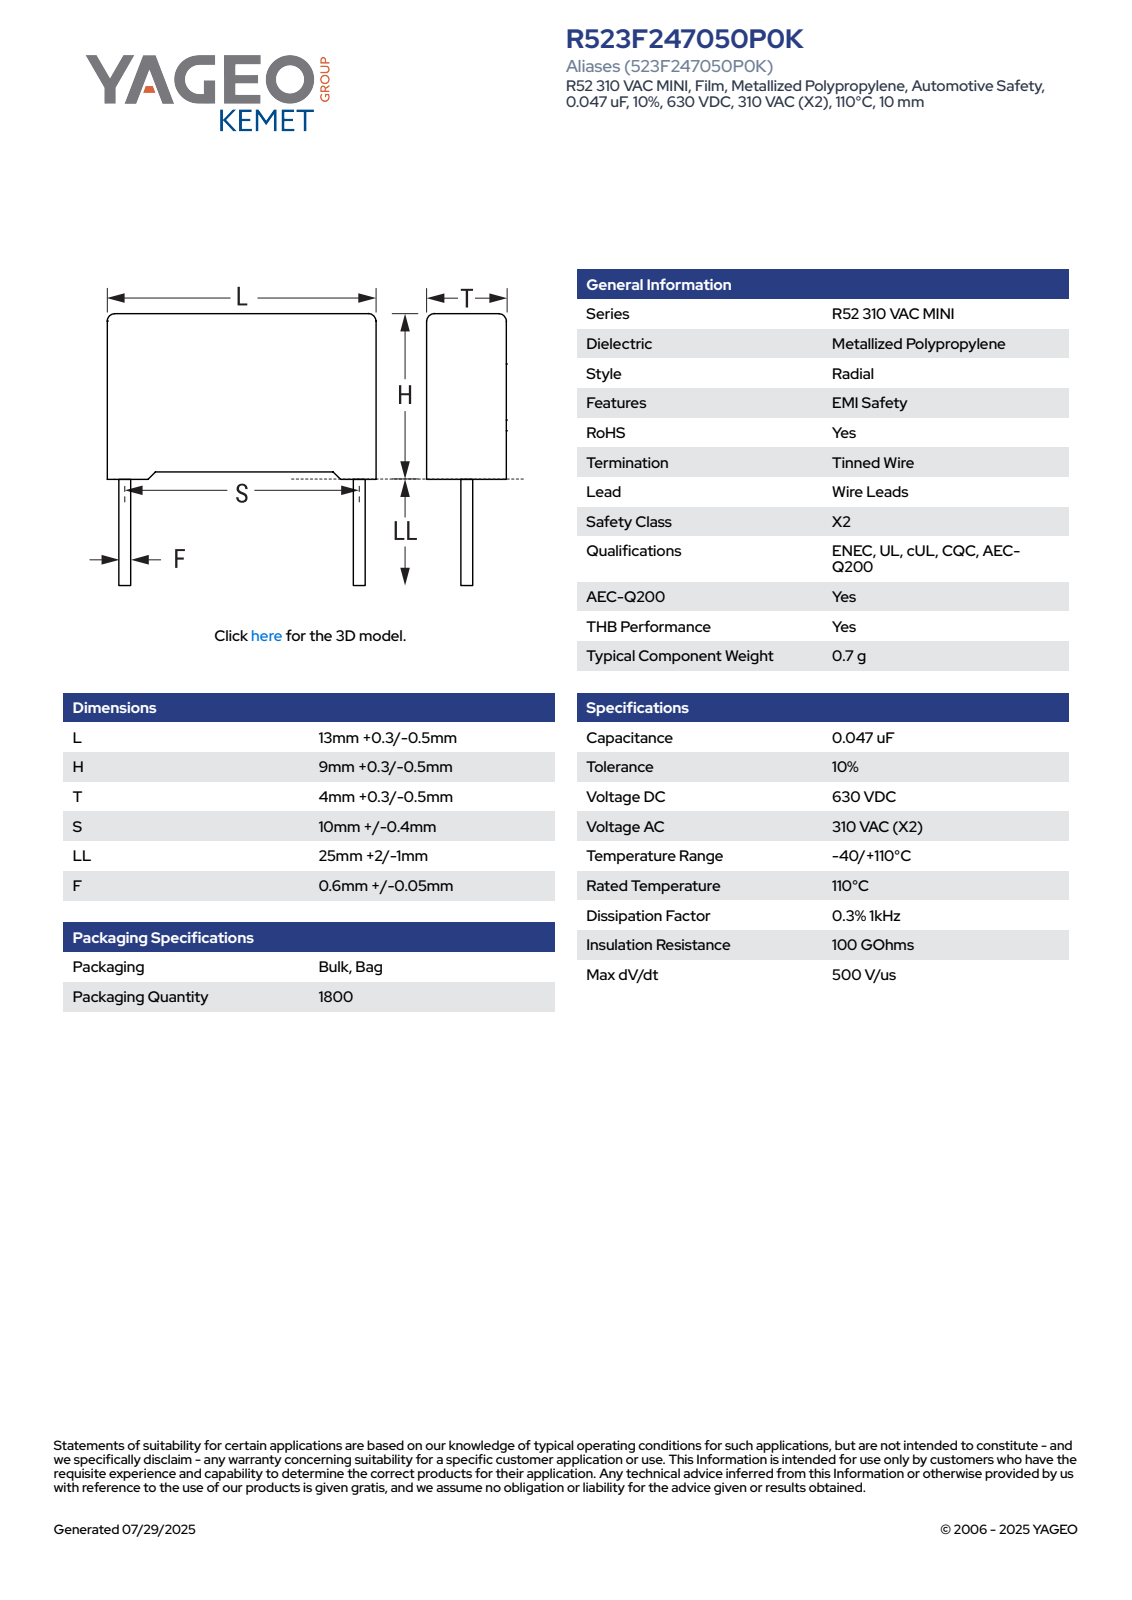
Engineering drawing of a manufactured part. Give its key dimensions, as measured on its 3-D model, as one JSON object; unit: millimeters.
{"part_name": "CFR_RB2_13X9X4_L13.3H9.3T4.3S10LL27F0.65", "step_written_by": "SolidWorks 2021 (AUTOMOTIVE_DESIGN)", "units": "millimeters", "bodies": {"solids": 4, "faces": 85, "planar": 77, "cylindrical": 8, "other": 0}, "overall_size": [36.3, 13.3, 4.3], "volume_mm3": 515, "surface_area_mm2": 576, "round_bosses_or_shafts": [[0.65, 2]], "partial_cylinders_radius": [[0.5, 4]], "face_to_face_distances": [4.3, 8.55, 13.3, 0.44, 3.86, 0.75, 9.3, 3.42, 0.32, 0.43]}
